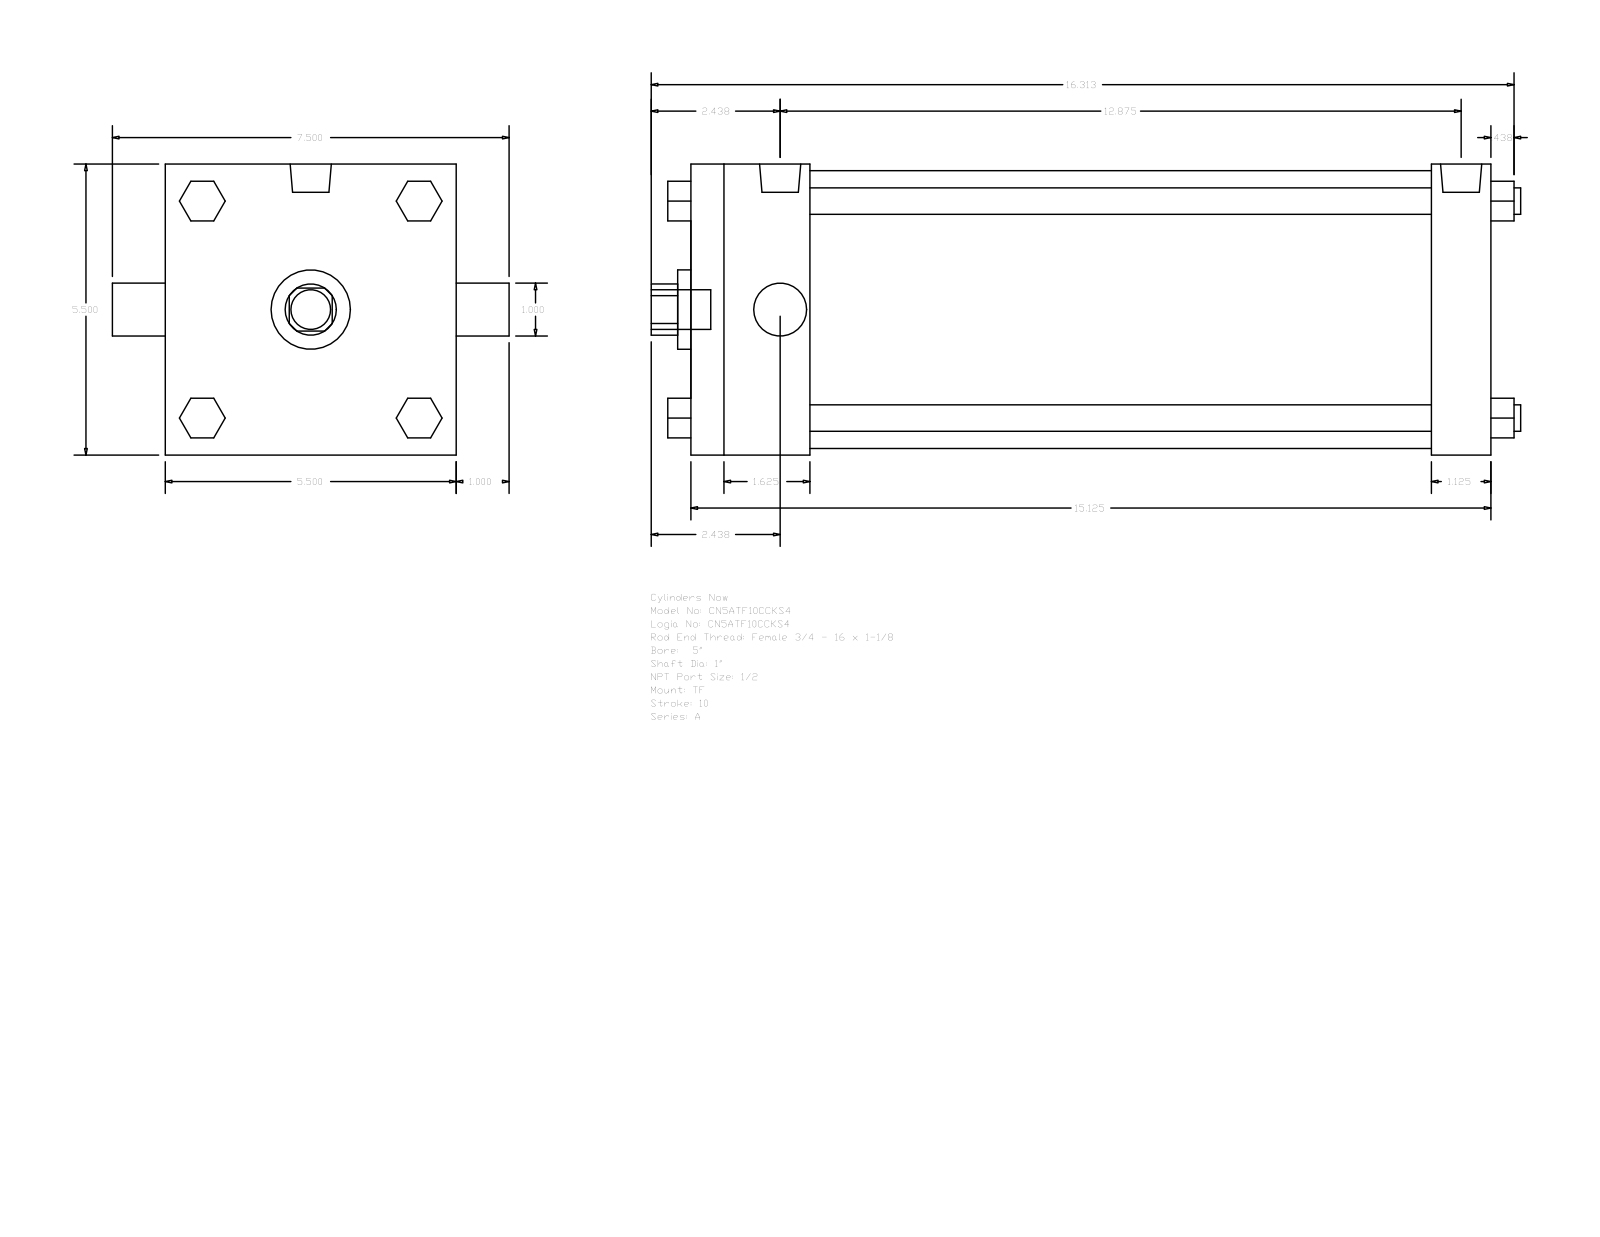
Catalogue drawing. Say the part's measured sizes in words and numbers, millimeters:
The part is named "A_TF__0500_1". Its 3-D file was written by "GSSL Pune (CONFIG_CONTROL_DESIGN)". It is 0 solids with 120 faces: 92 planar, 28 cylindrical and 0 other. Overall it measures 417.51 by 190.5 by 139.7 millimeters. Round holes: 2 of diameter 25.4, 1 of diameter 38.1, 1 of diameter 133.35. Round bosses or shafts: 4 of diameter 12.7, 3 of diameter 8.73, 2 of diameter 19.77, 1 of diameter 19.05. Partial cylindrical surfaces (rounded edges, fillets, slot ends): 1 of radius 12.29. The main face-to-face distances are 139.7, 384.18, 355.6, 28.58, 57.15, 298.45, 327.03, 19.05, 52.07, 90.18.
